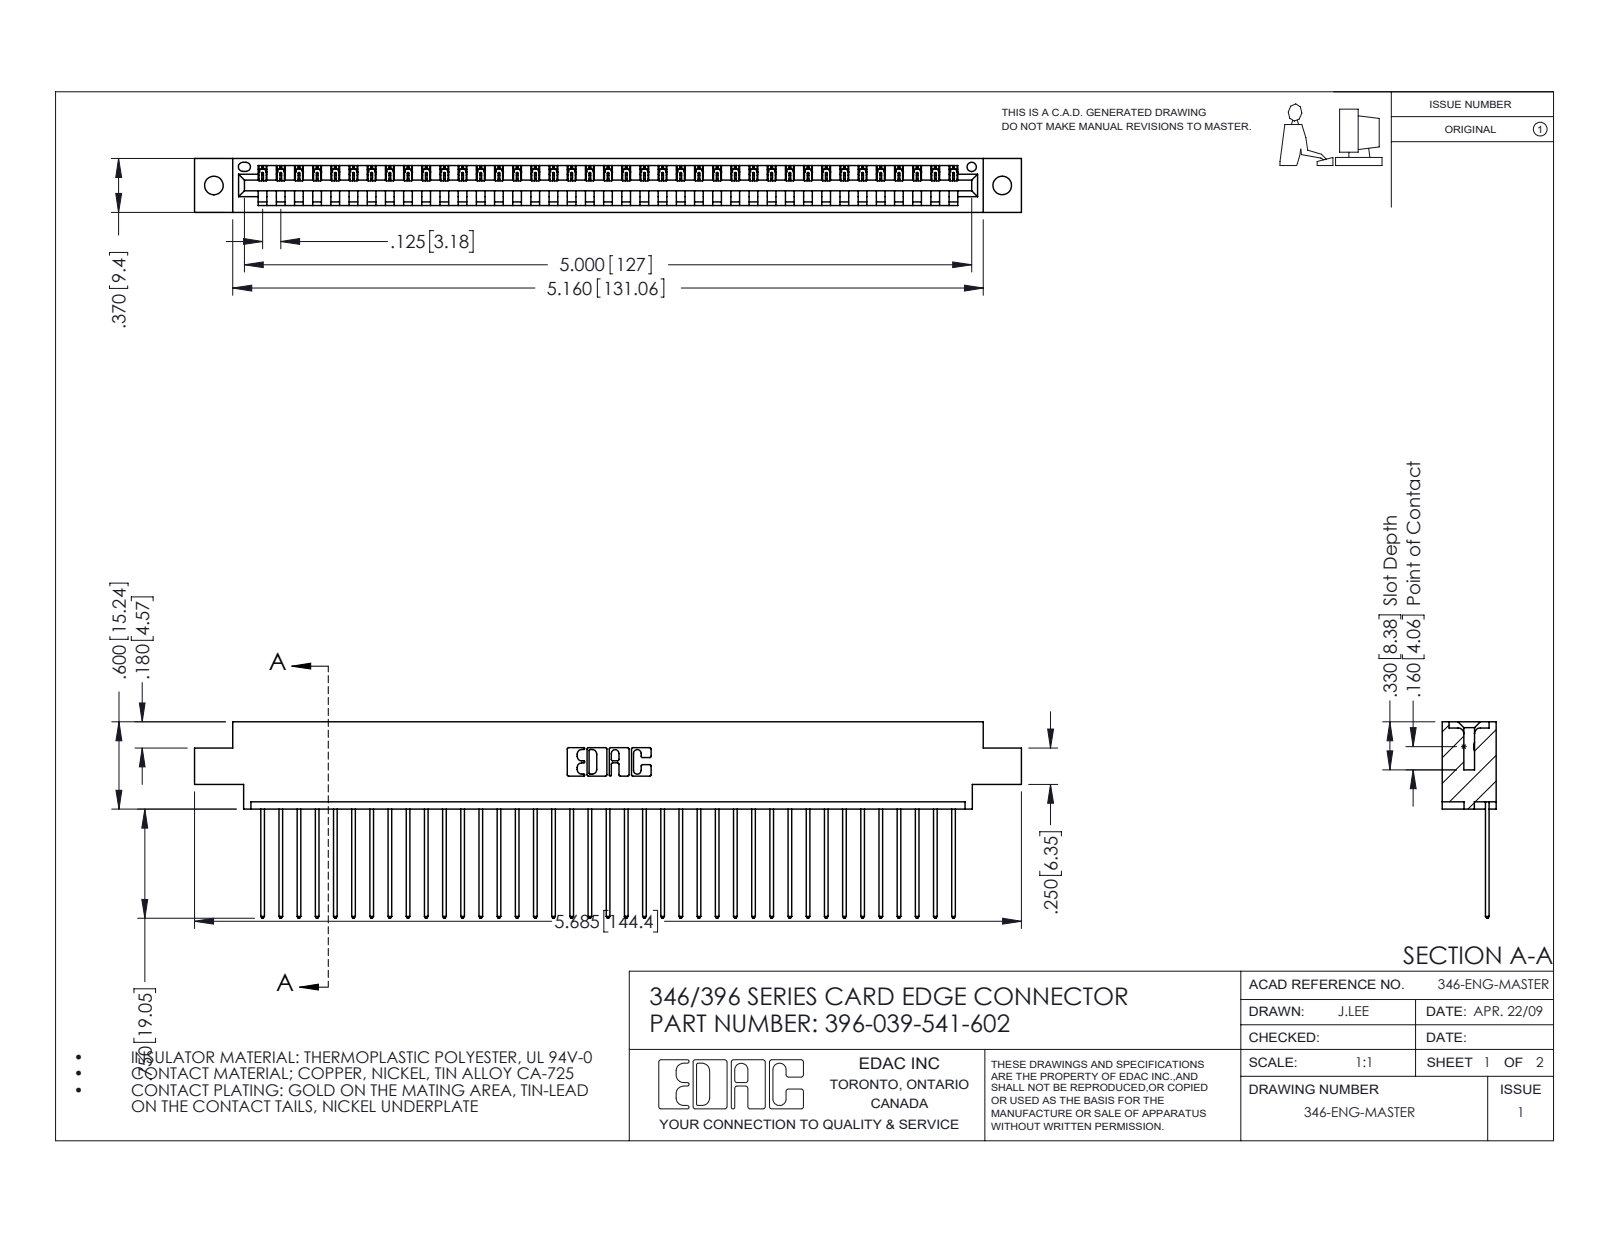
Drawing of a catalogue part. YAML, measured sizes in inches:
part_name: "345-292-001_345-293-141; 396-039-541-602; 346 Part_0.170 Offset - 0.128 Dia"
step_written_by: "SolidWorks 2016 (CONFIG_CONTROL_DESIGN)"
units: inches
bodies: {solids: 40, faces: 2388, planar: 1640, cylindrical: 748, other: 0}
overall_size: [5.685, 1.35, 0.37]
volume: 0.838
surface_area: 27.59
round_holes:
  - {diameter: 0.128, count: 2}
  - {diameter: 0.064, count: 1}
partial_cylinders:
  - {radius: 0.006, count: 78}
  - {radius: 0.01, count: 78}
  - {radius: 0.01, count: 22}
  - {radius: 0.007, count: 6}
  - {radius: 0.031, count: 6}
  - {radius: 0.026, count: 3}
  - {radius: 0.031, count: 2}
  - {radius: 0.04, count: 2}
face_to_face_distances: [0.048, 0.322, 0.37, 0.25, 0.072, 0.298, 0.025, 0.148, 0.222, 0.1]
hole_center_spacings: [0.246, 5.211, 5.42]
